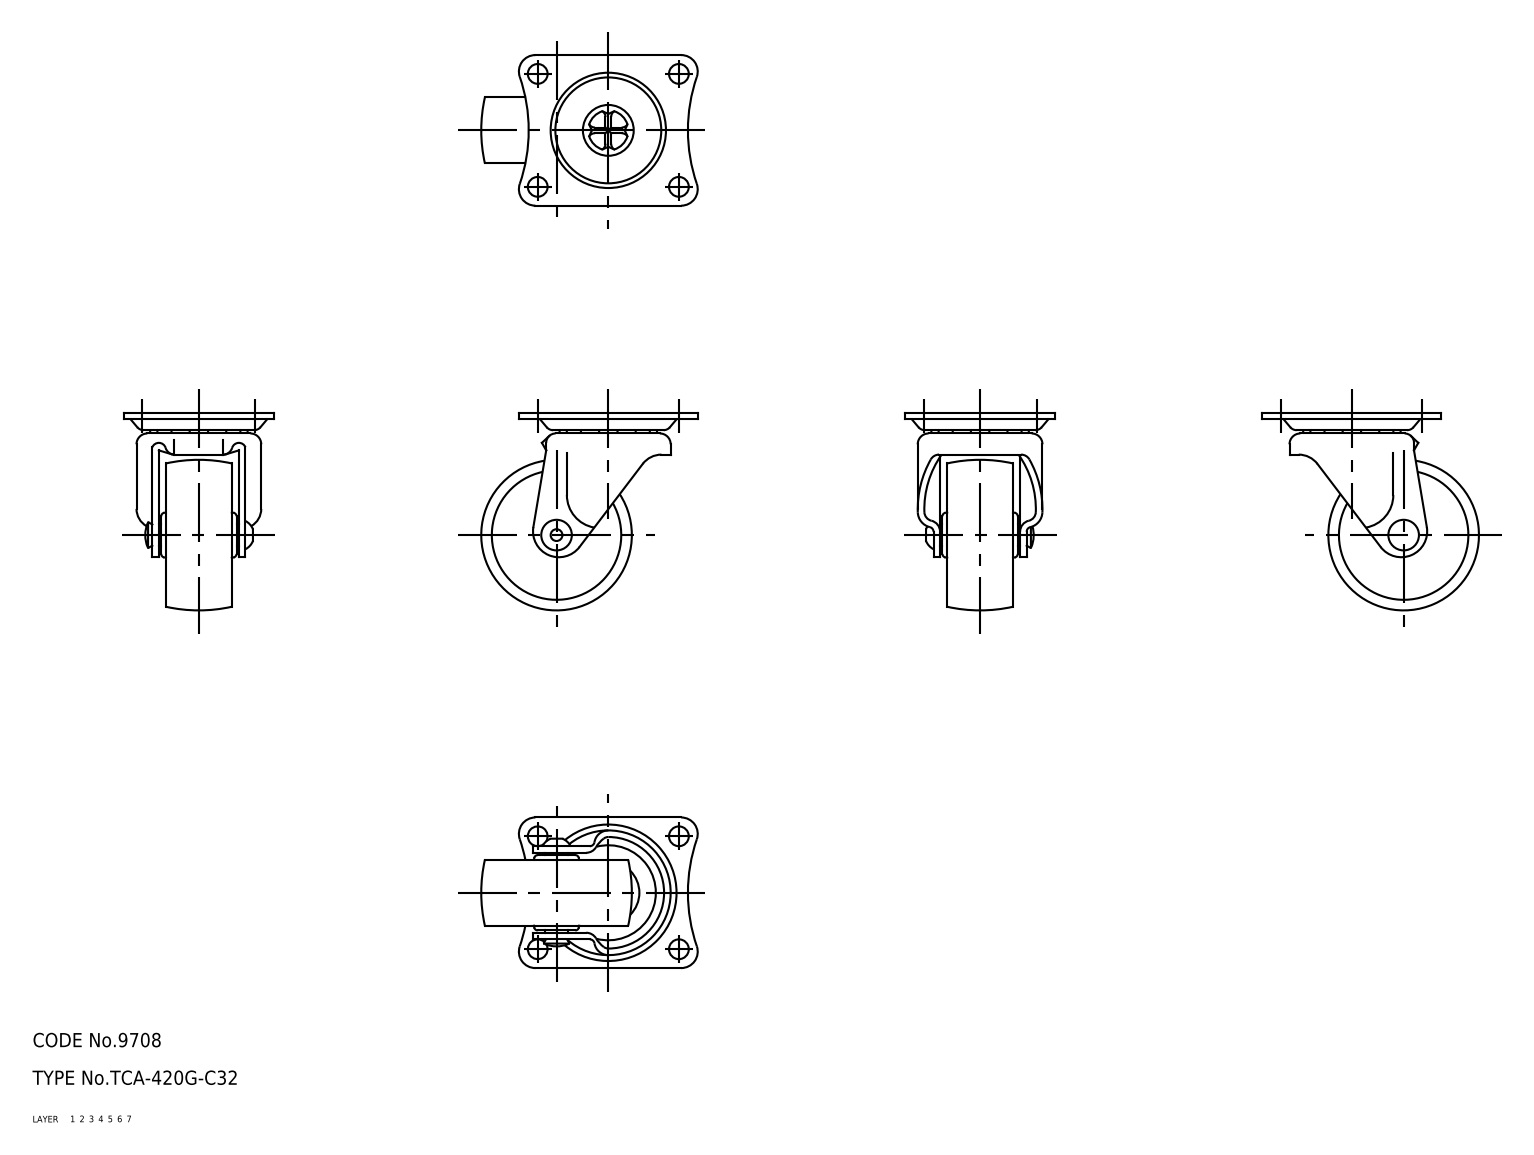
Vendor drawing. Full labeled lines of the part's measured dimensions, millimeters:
Part name (STEP PRODUCT): wheel; mounting plate; main shaft; axle (+1 more)
STEP written by: CADfix (AUTOMOTIVE_DESIGN)
Units: millimetres
Bodies: 5 solids, 239 faces (0 planar, 0 cylindrical, 239 other)
Overall size (bounding box): 46 × 42 × 32
Volume: 12 921 mm³ · Surface area: 10 667 mm²
